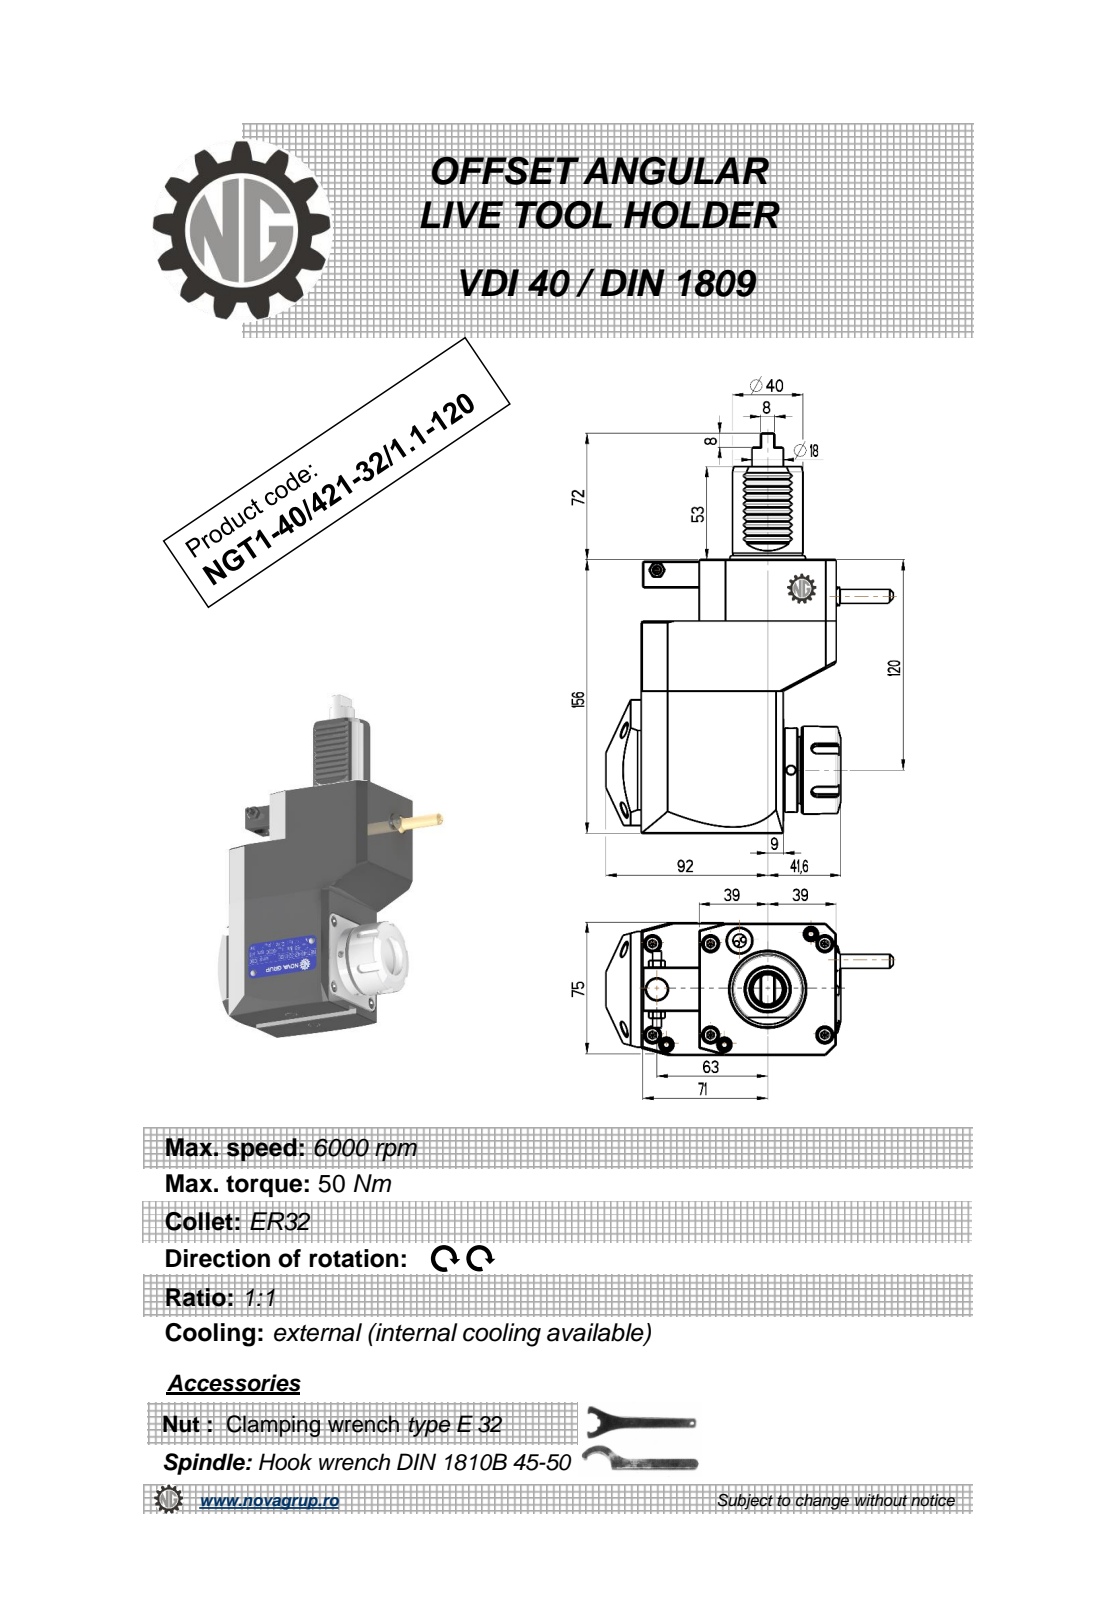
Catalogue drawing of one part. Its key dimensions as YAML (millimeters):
part_name: "NGT1_40_421_32_1_1_120"
step_written_by: "PRO/ENGINEER BY PARAMETRIC TECHNOLOGY CORPORATION, 2010280 (CONFIG_CONTROL_DESIGN)"
units: millimeters
bodies: {solids: 1, faces: 427, planar: 211, cylindrical: 89, other: 127}
overall_size: [228, 163.5, 76.6]
volume: 1183000
surface_area: 87309
round_holes:
  - {diameter: 5, count: 3}
  - {diameter: 3, count: 1}
  - {diameter: 4.2, count: 1}
  - {diameter: 9.5, count: 1}
  - {diameter: 12, count: 1}
  - {diameter: 27, count: 1}
round_bosses_or_shafts:
  - {diameter: 50, count: 1}
  - {diameter: 48, count: 1}
  - {diameter: 41, count: 1}
  - {diameter: 40, count: 1}
  - {diameter: 17.8, count: 1}
  - {diameter: 11.2, count: 1}
  - {diameter: 8.96, count: 1}
  - {diameter: 8, count: 1}
partial_cylinders:
  - {radius: 0.26, count: 12}
  - {radius: 0.3, count: 10}
  - {radius: 0.22, count: 6}
  - {radius: 3, count: 5}
  - {radius: 0.8, count: 2}
  - {radius: 0.5, count: 1}
  - {radius: 40, count: 1}
face_to_face_distances: [75, 156, 111, 35, 121, 30, 81, 33, 48, 78]
hole_center_spacings: [20.93, 76.25, 100.28, 112.5, 137.15]
